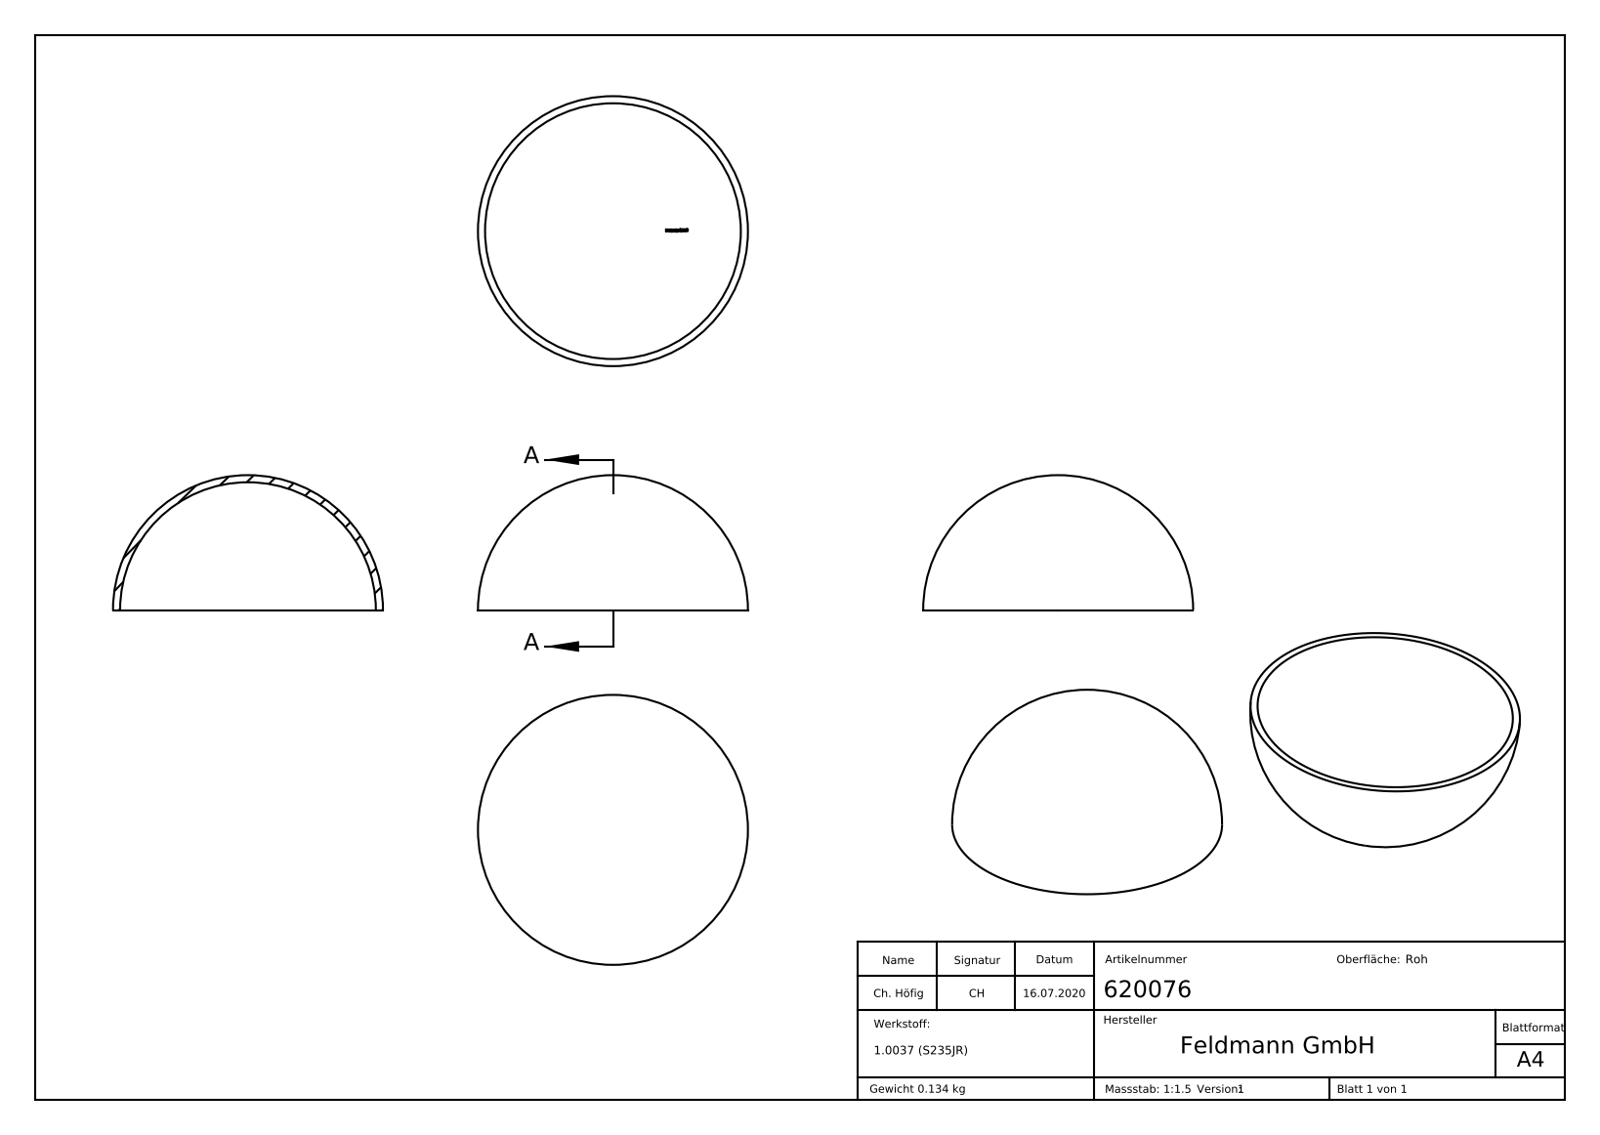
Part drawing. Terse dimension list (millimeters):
name: 620076
written by: SolidWorks 2018 (CONFIG_CONTROL_DESIGN)
unit: mm
bodies: 1 solid, 186 faces (73 planar, 0 cylindrical, 113 other)
size: 76 × 76 × 38
volume: 17 207 mm³; area: 17 685 mm²
face distances: 1.19, 0.55, 0.5, 0.53, 0.81, 0.45, 0.66, 1.74, 1.31, 1.47
